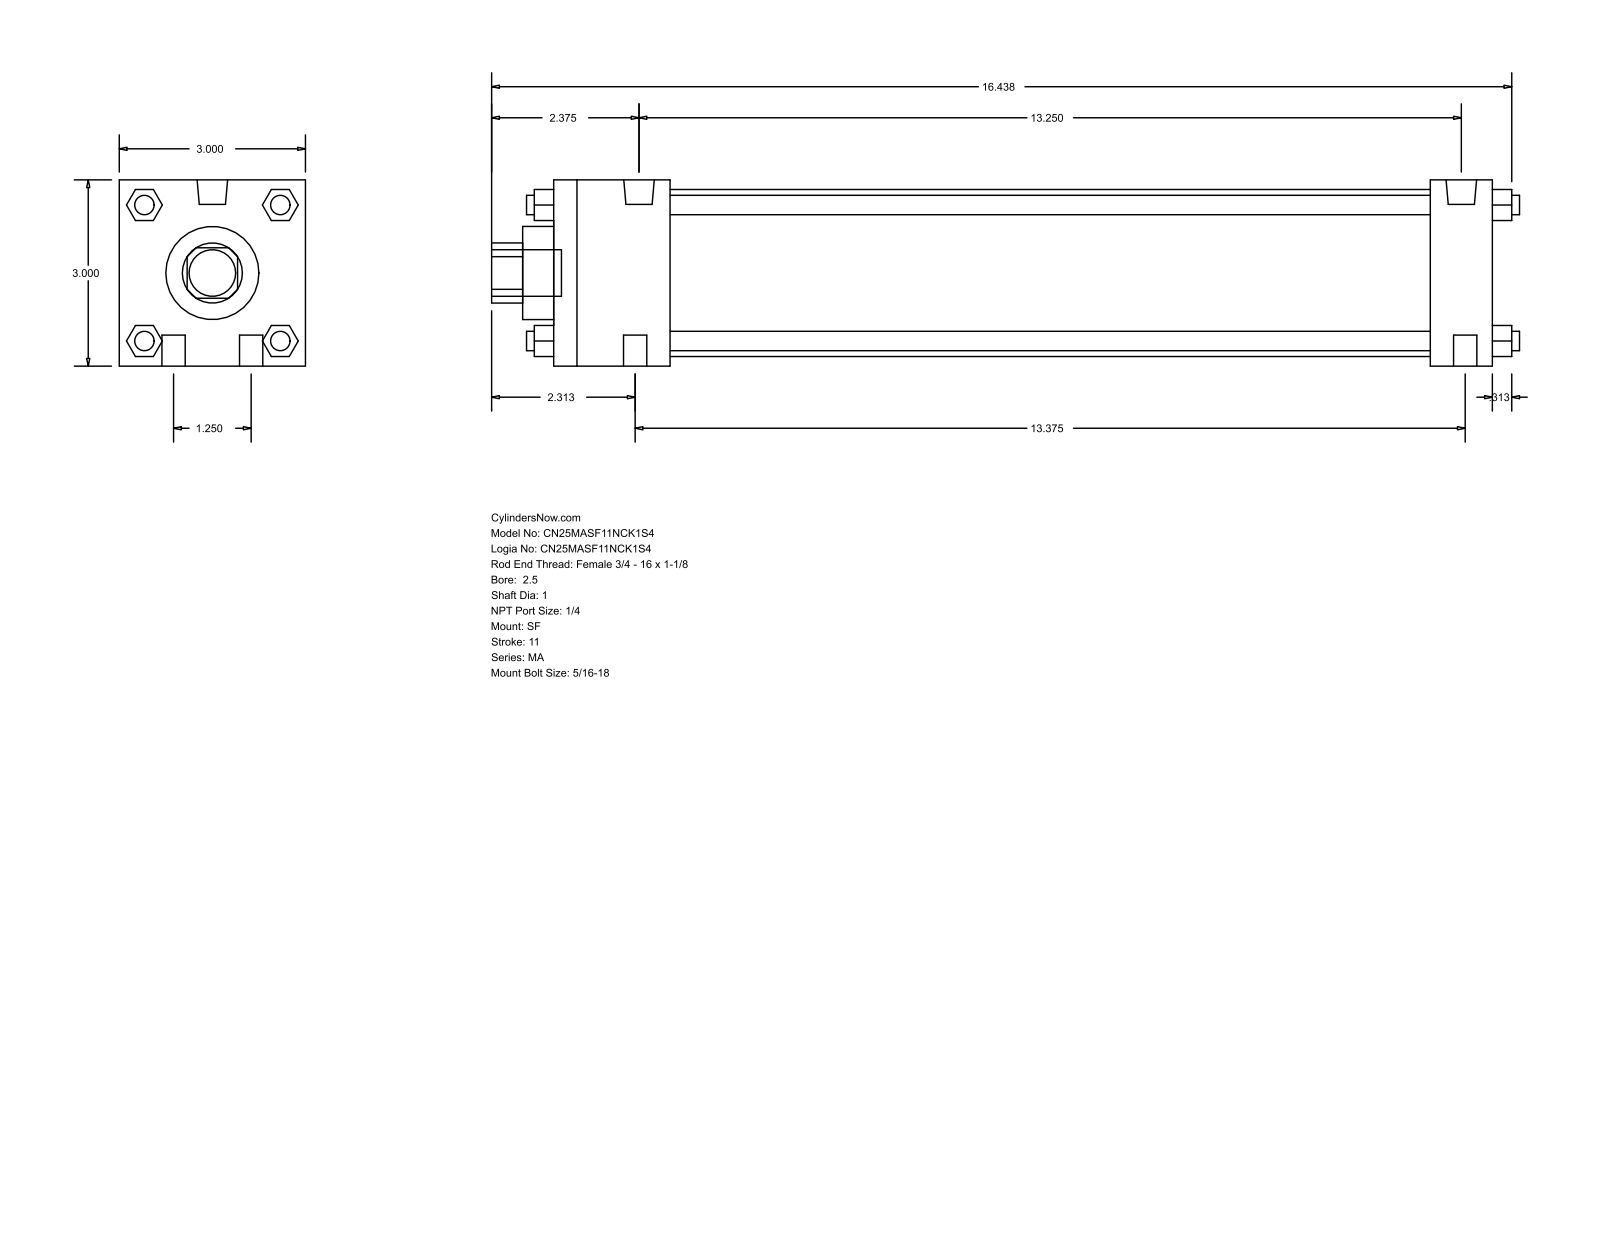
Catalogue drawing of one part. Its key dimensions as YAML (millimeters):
part_name: "MA_SF__0250_1"
step_written_by: "GSSL Pune (CONFIG_CONTROL_DESIGN)"
units: millimeters
bodies: {solids: 0, faces: 124, planar: 94, cylindrical: 30, other: 0}
overall_size: [420.69, 76.2, 76.2]
round_holes:
  - {diameter: 25.4, count: 1}
  - {diameter: 38.1, count: 1}
  - {diameter: 68.33, count: 1}
round_bosses_or_shafts:
  - {diameter: 7.94, count: 6}
  - {diameter: 9.53, count: 4}
  - {diameter: 12.49, count: 2}
  - {diameter: 19.05, count: 1}
partial_cylinders:
  - {radius: 12.29, count: 1}
face_to_face_distances: [76.2, 384.17, 12.7, 358.78, 25.39, 47.63, 311.15, 336.54, 27.81, 48.17]
